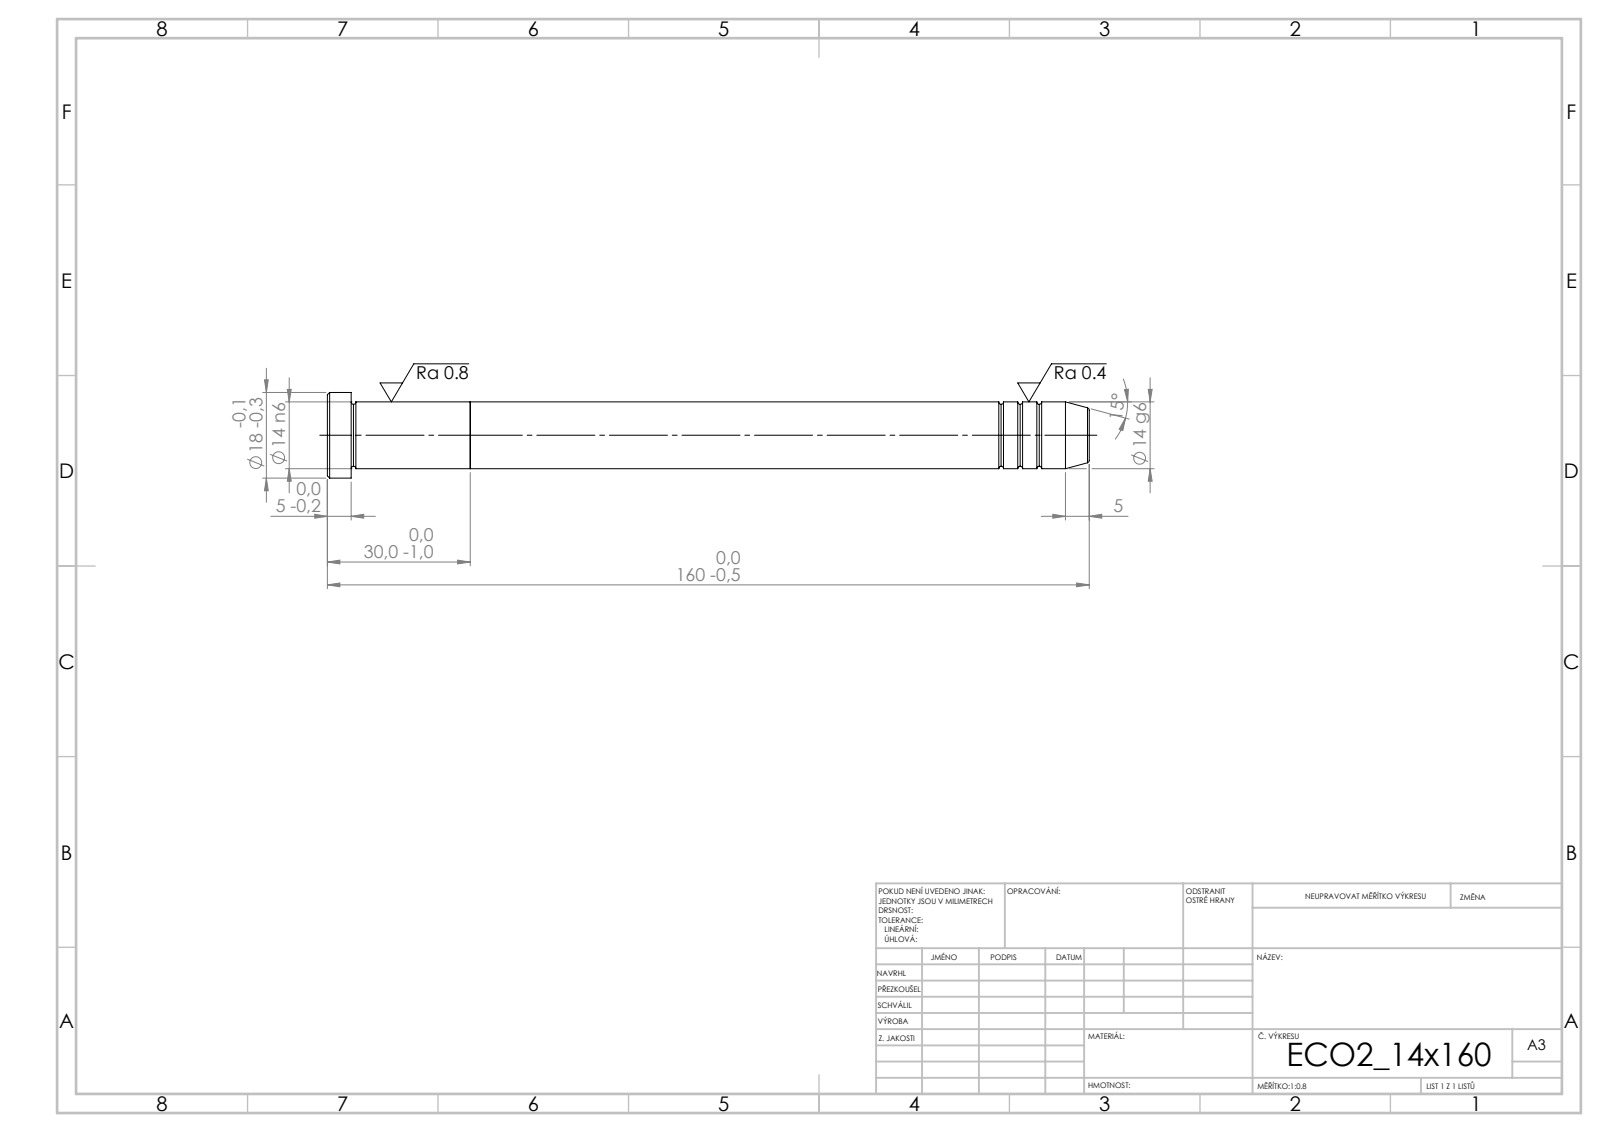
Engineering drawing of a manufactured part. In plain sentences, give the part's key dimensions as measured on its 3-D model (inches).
Its 3-D file was written by "SolidWorks 2019 (CONFIG_CONTROL_DESIGN)". It is 2 solids with 39 faces: 5 planar, 12 cylindrical and 22 other. Overall it measures 6.299 by 0.709 by 0.709 inches. Its volume is 1.521 cubic inches and its surface area 12.27 square inches. Round bosses or shafts: 1 of diameter 0.709, 1 of diameter 0.551. The main face-to-face distances are 1.181, 0.984, 0.197, 5.118, 6.102, 6.299.
